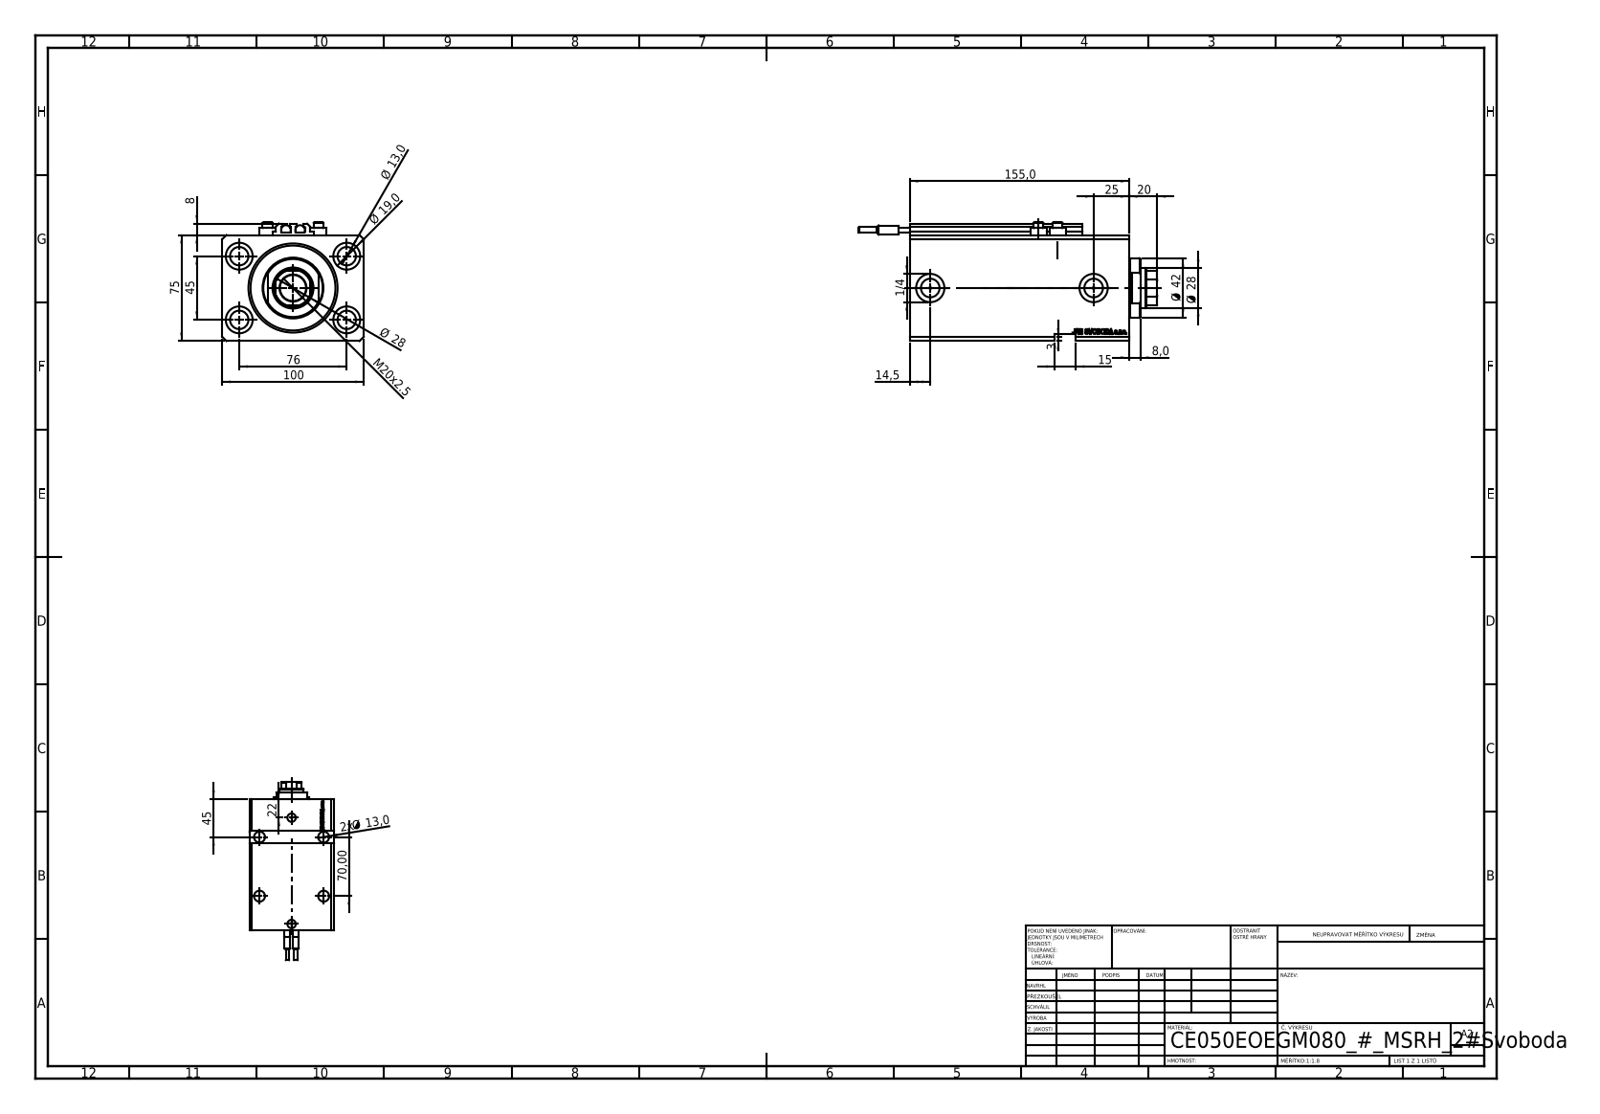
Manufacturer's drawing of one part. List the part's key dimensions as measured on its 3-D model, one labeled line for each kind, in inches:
Part name (STEP PRODUCT): V250CE_C_VCP; V250CE_VC_E; ALLEN BOLT V250CE; V250CE_E_Body (+1 more)
STEP written by: SolidWorks 2019 (CONFIG_CONTROL_DESIGN)
Units: inches
Bodies: 10 solids, 1160 faces (567 planar, 158 cylindrical, 435 other)
Overall size (bounding box): 8.307 × 3.937 × 3.307
Volume: 57.62 in³ · Surface area: 276.9 in²
Round holes (diameter × count): ⌀0.512 ×8, ⌀0.049 ×4, ⌀0.157 ×4, ⌀0.748 ×4, ⌀0.394 ×2, ⌀0.518 ×2, ⌀0.787 ×2, ⌀0.728 ×1, ⌀1.102 ×1, ⌀1.969 ×1, ⌀2.48 ×1
Round bosses / shafts (diameter × count): ⌀0.457 ×4, ⌀0.276 ×4, ⌀0.268 ×2, ⌀0.256 ×2, ⌀0.157 ×2, ⌀1.654 ×1
Partial cylindrical surfaces — rounded edges, fillets, slot ends (radius × count): R0.008 ×10, R0.531 ×1
Main face-to-face distances: 2.953, 3.937, 6.102, 0.787, 0.469, 5.634, 5.315, 4.846, 3.15, 0.197
Hole centre spacings: 1.739, 2.992, 0.535, 0.816, 1.086, 1.324, 1.417, 1.515
